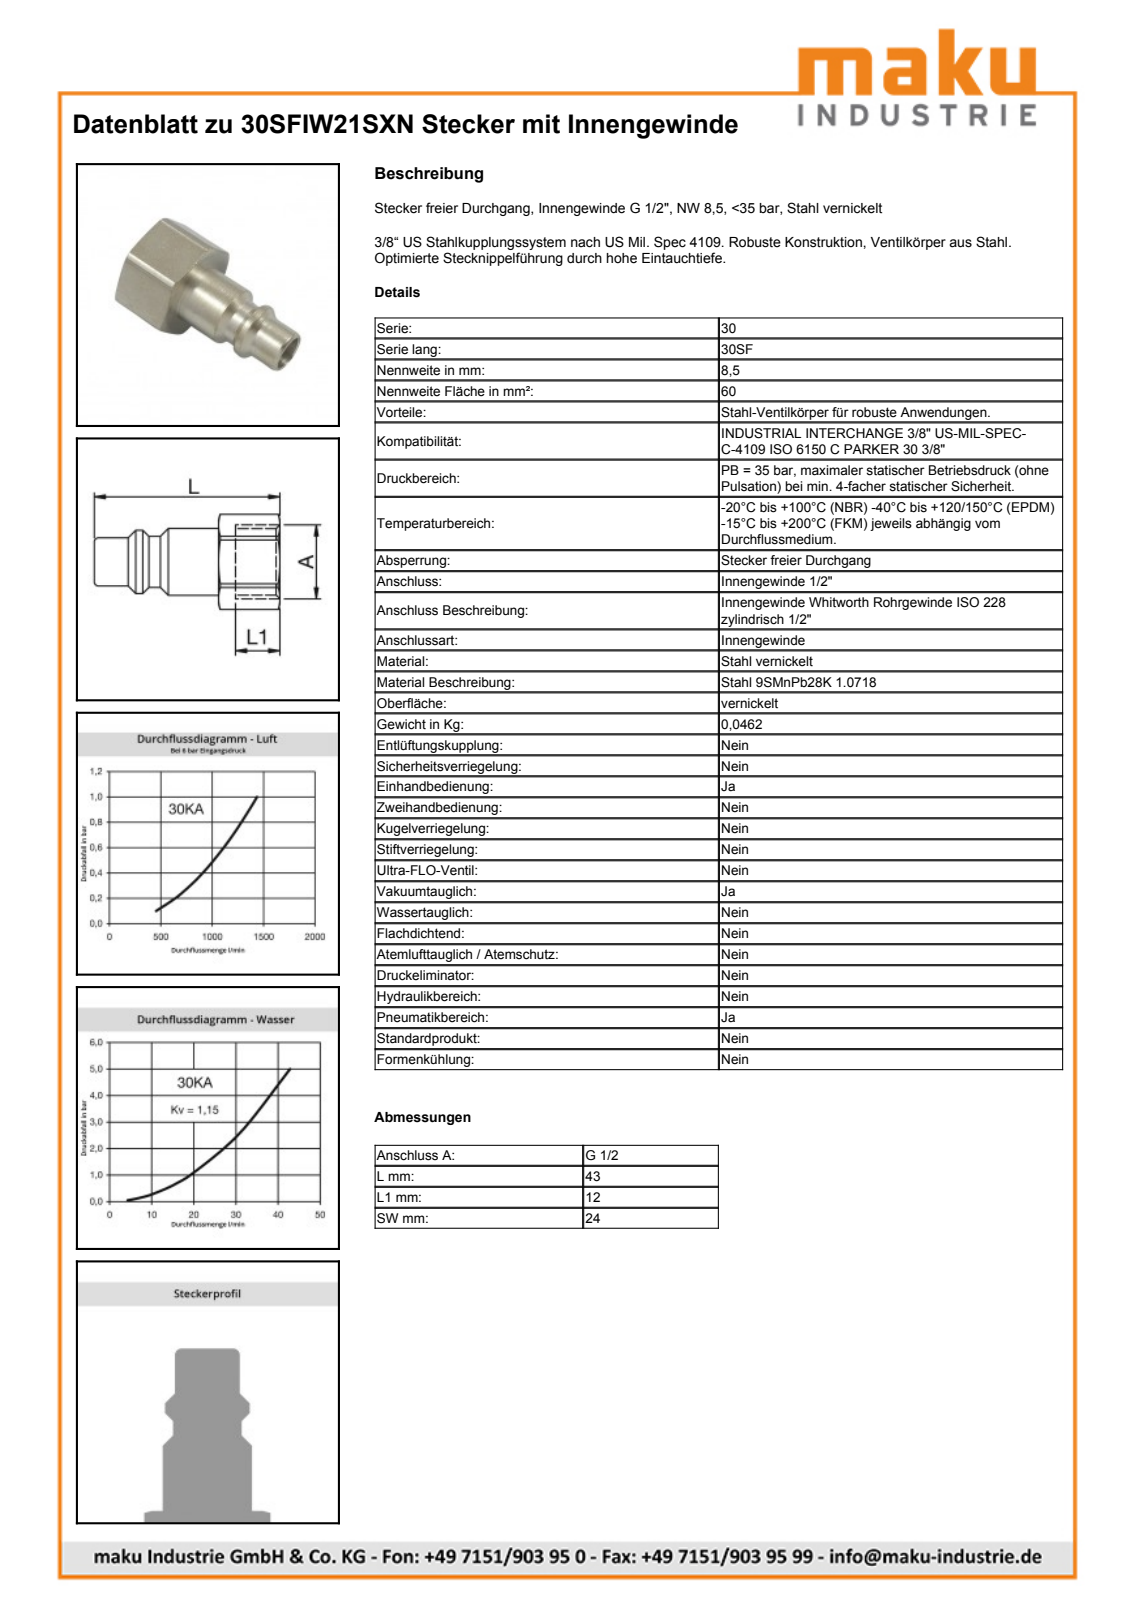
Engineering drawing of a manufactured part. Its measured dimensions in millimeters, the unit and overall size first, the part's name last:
Units: millimetres
Overall size (bounding box): 43.3 × 27.05 × 24
Round holes (diameter × count): ⌀8.2 ×1, ⌀20.95 ×1
Round bosses / shafts (diameter × count): ⌀15.05 ×1, ⌀14.25 ×1, ⌀11.5 ×1, ⌀10.85 ×1
Partial cylindrical surfaces — rounded edges, fillets, slot ends (radius × count): R13.53 ×1
Main face-to-face distances: 24, 3.3, 15.3, 12, 28, 31.3, 43.3
Volume: 5 639 mm³ · Surface area: 4 813 mm²
Bodies: 1 solid, 39 faces (10 planar, 12 cylindrical, 17 other)
Part name (STEP PRODUCT): D103005
STEP written by: Autodesk Inventor 2011 (AUTOMOTIVE_DESIGN)
